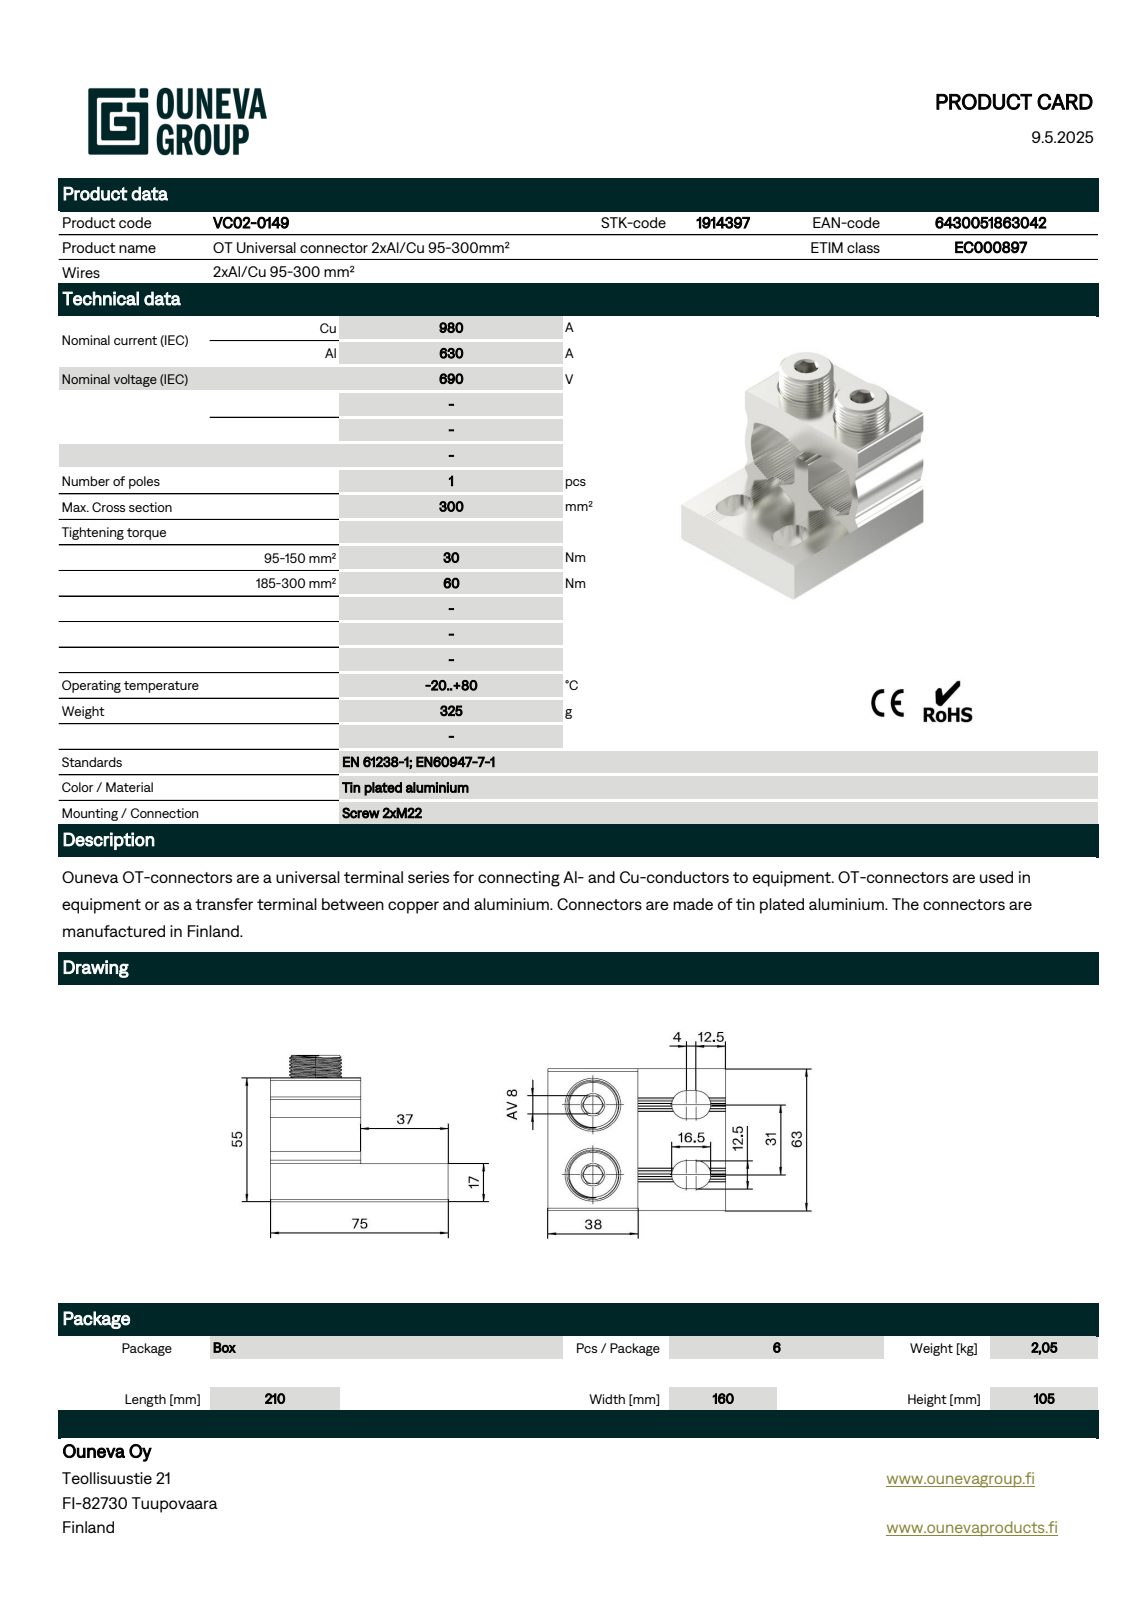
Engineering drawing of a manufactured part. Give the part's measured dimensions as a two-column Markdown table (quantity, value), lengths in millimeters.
| quantity | value |
| --- | --- |
| part name | Liitinrunko OT 2x95-300 |
| STEP written by | Creo Elements/Direct Modeling 20.6A 14-Oct-2023 (C) Parametric Technology GmbH (AUTOMOTIVE_DESIGN) |
| units | millimeters |
| bodies | 1 solid, 296 faces (147 planar, 133 cylindrical, 16 other) |
| overall size | 75 × 65 × 63 |
| volume | 127 079 mm³ |
| surface area | 29 333 mm² |
| round bosses / shafts (diameter × count) | 22 × 2 |
| partial cylindrical surfaces (radius × count) | 0.3 × 82, 1 × 4, 1.14 × 4, 2.27 × 4, 6.25 × 4, 1.5 × 2, 1.7 × 2, 3.97 × 2 |
| main face-to-face distances | 38, 17, 55, 63, 37, 75, 65, 48, 10, 35.28 |
